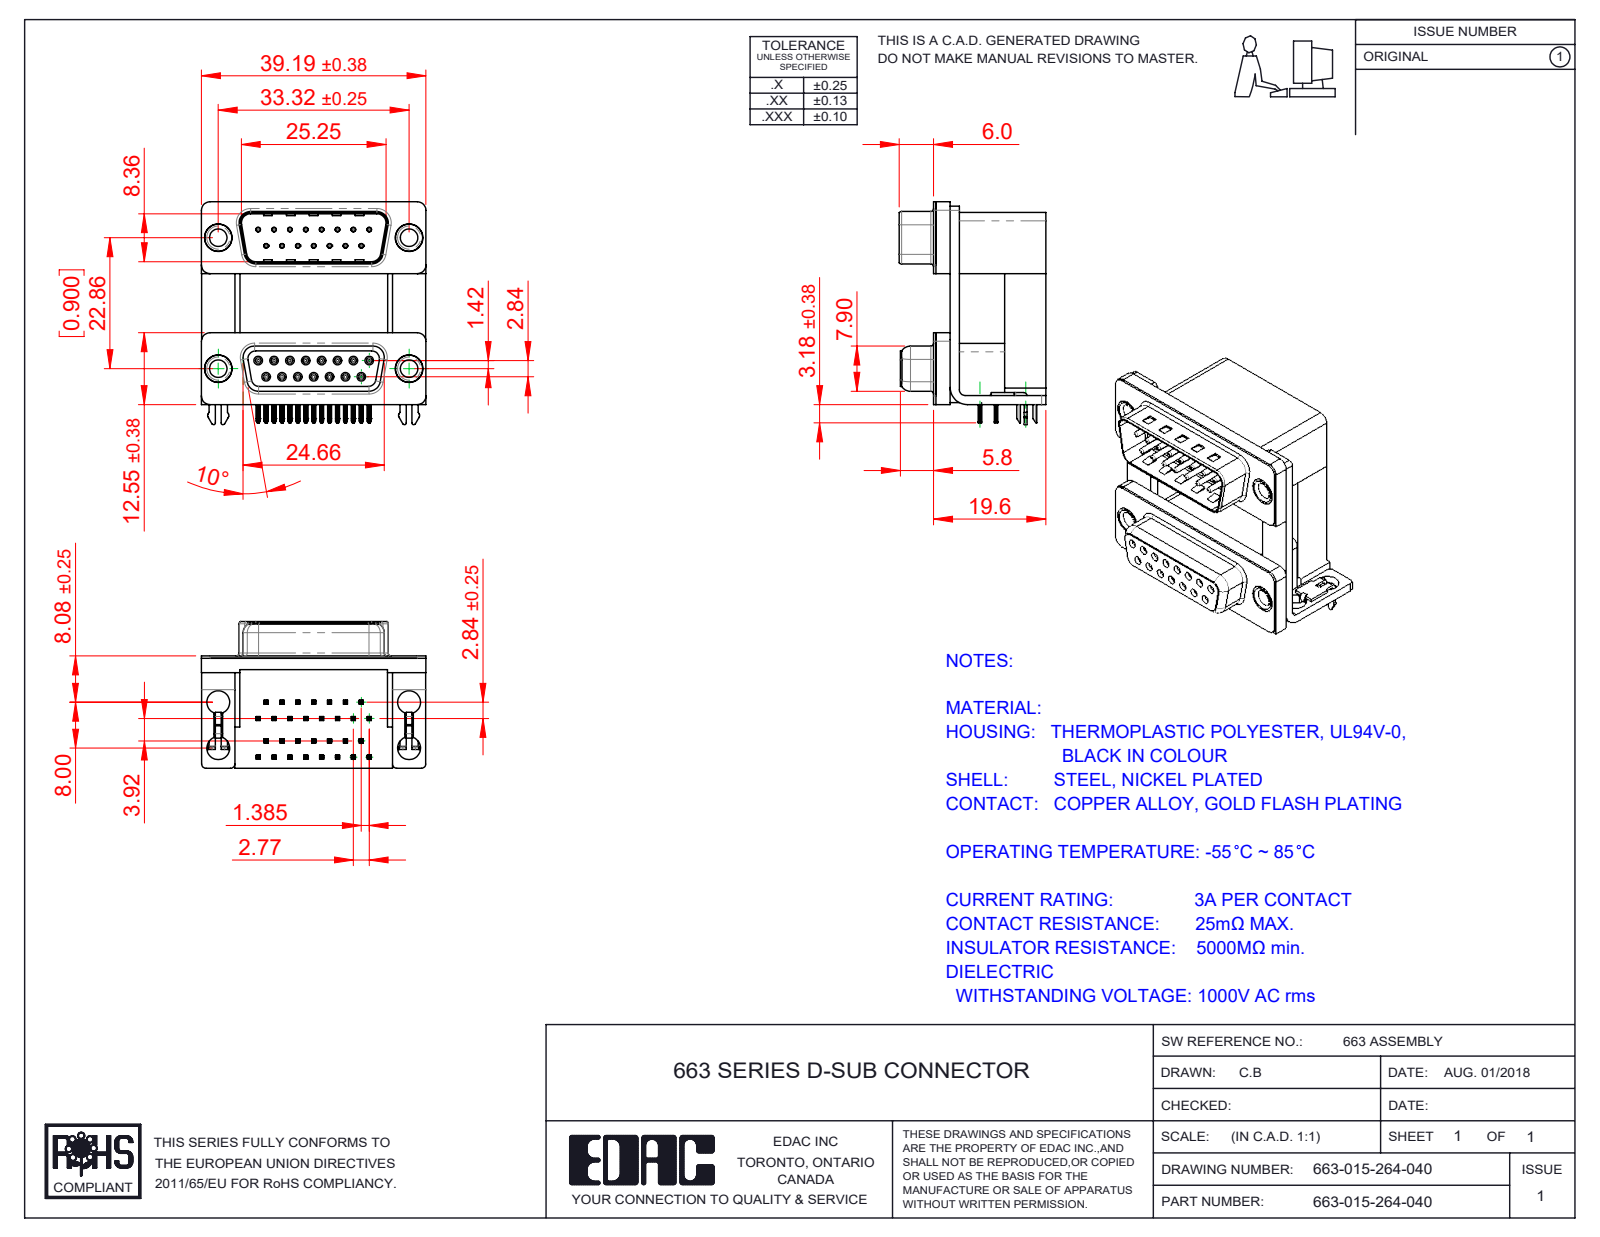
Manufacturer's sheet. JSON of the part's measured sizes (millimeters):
{"part_name": "663 2 Prong Board Lock_4; 663 Shell Plug_15 Contacts; 663 Housing Lower_15 Contacts; 663 Contact Top Lower (+8 more)", "step_written_by": "SolidWorks 2020 (CONFIG_CONTROL_DESIGN)", "units": "millimeters", "bodies": {"solids": 43, "faces": 3936, "planar": 2093, "cylindrical": 1008, "other": 835}, "overall_size": [39.19, 38.91, 25.6], "volume_mm3": 15963, "surface_area_mm2": 17562, "round_holes": [[0.8, 30], [0.35, 15], [0.9, 15], [4, 8], [3.05, 4], [3.5, 4], [4.8, 4], [5, 4]], "round_bosses_or_shafts": [[1.2, 15], [0.75, 15], [4.9, 4], [4.75, 4], [3.85, 4]], "partial_cylinders_radius": [[0.1, 121], [0.25, 66], [0.15, 60], [0.12, 30], [0.35, 30], [0.5, 16], [1.5, 16], [0.34, 15]], "face_to_face_distances": [19.2, 0.4, 12, 7.2, 16.7, 9.5, 2.5, 10.7, 12.4, 1.6], "hole_center_spacings": [3.16, 23.03, 2.77, 23.52, 5.54, 8.31, 22.86, 24.32]}
